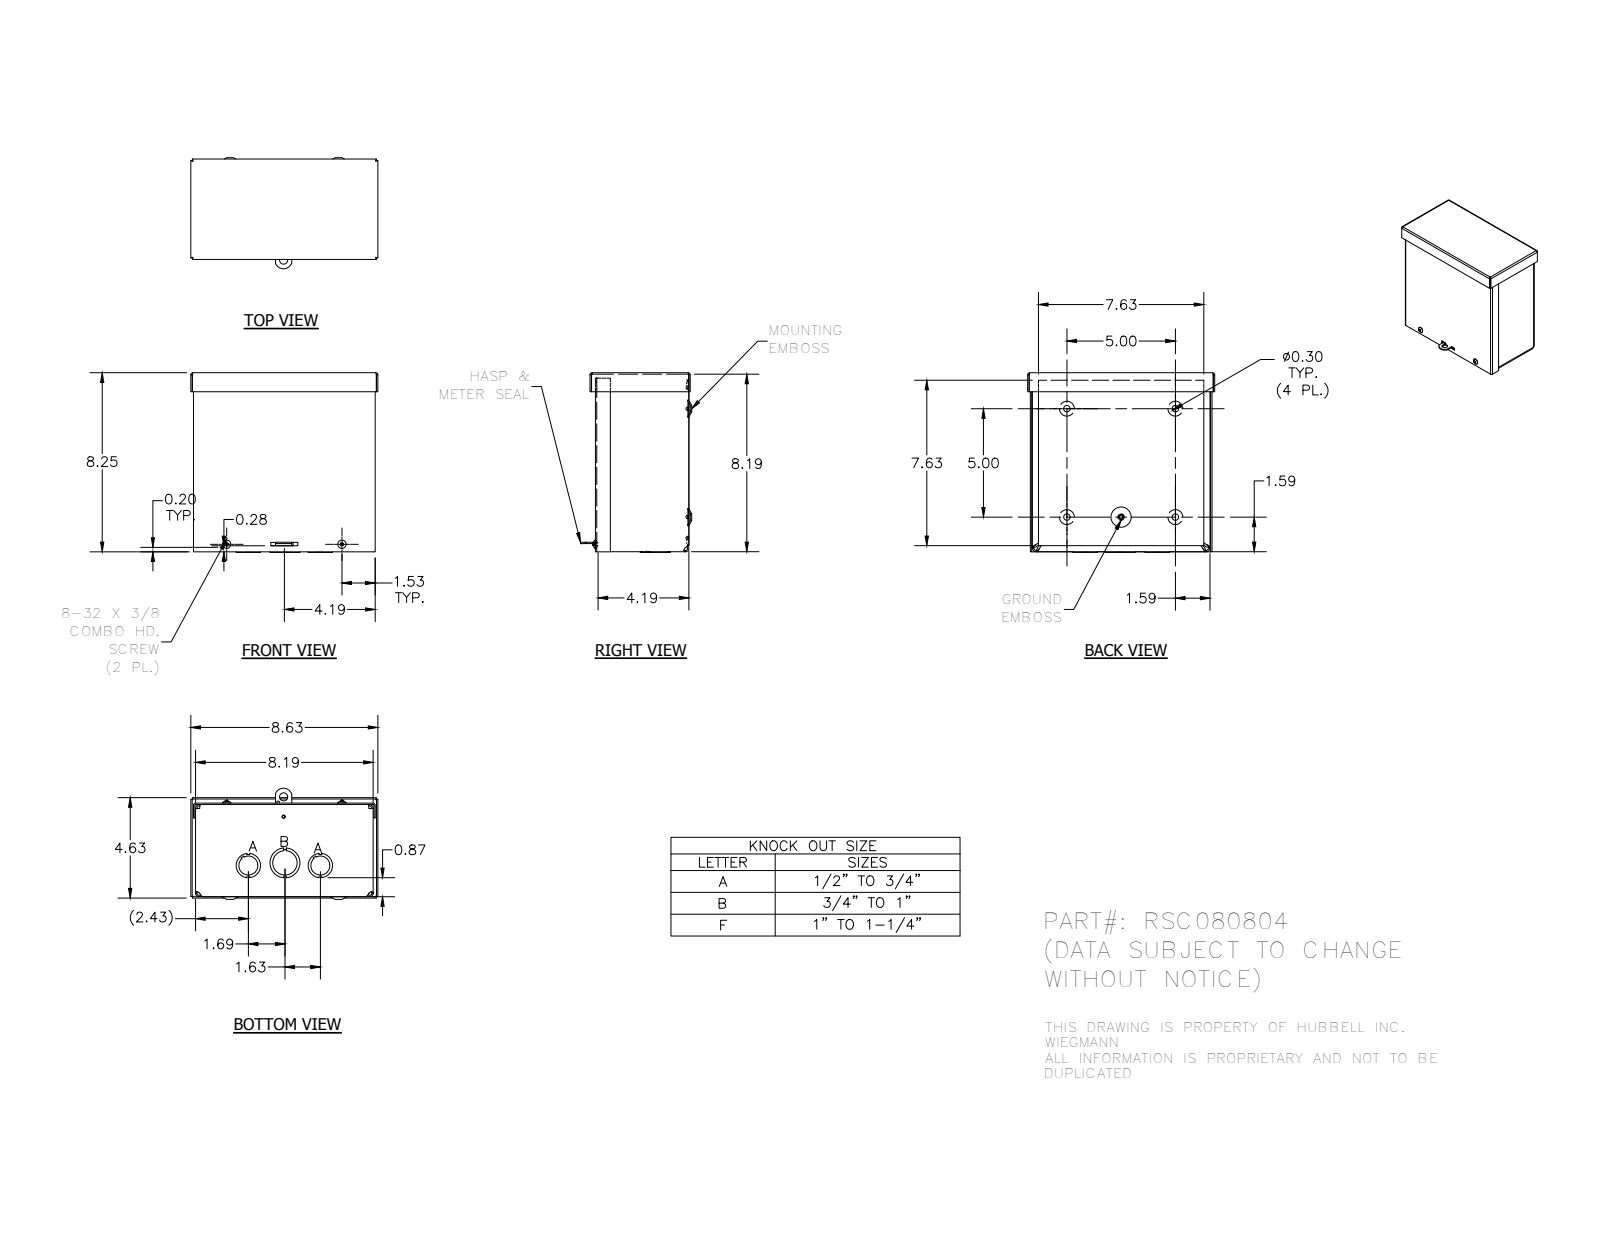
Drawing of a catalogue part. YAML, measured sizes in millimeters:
part_name: "RSC080804; RSC080804_WRAP; RSC0808_LID; RSC0804_CAP (+4 more)"
step_written_by: "Autodesk Inventor 2012 (AUTOMOTIVE_DESIGN)"
units: millimeters
bodies: {solids: 7, faces: 503, planar: 238, cylindrical: 121, other: 144}
overall_size: [219.1, 210.3, 130.2]
volume: 380700
surface_area: 492100
round_holes:
  - {diameter: 7.6, count: 4}
  - {diameter: 8, count: 4}
  - {diameter: 28.6, count: 3}
  - {diameter: 3.2, count: 2}
  - {diameter: 3.8, count: 2}
  - {diameter: 22.2, count: 2}
  - {diameter: 4, count: 1}
  - {diameter: 4.2, count: 1}
  - {diameter: 9.5, count: 1}
  - {diameter: 34.9, count: 1}
round_bosses_or_shafts:
  - {diameter: 9.8, count: 2}
  - {diameter: 4.2, count: 2}
  - {diameter: 5.8, count: 1}
partial_cylinders:
  - {radius: 0.3, count: 10}
  - {radius: 0.8, count: 8}
  - {radius: 2.4, count: 8}
  - {radius: 3.2, count: 8}
  - {radius: 4.7, count: 8}
  - {radius: 0.5, count: 4}
  - {radius: 0.8, count: 4}
  - {radius: 1.4, count: 4}
face_to_face_distances: [1.6, 206.4, 1.6, 107.9, 106.3, 208, 1.6, 3.1, 109.5, 108]
hole_center_spacings: [127, 27.2, 32, 63.5, 135, 142, 154, 158.8]
